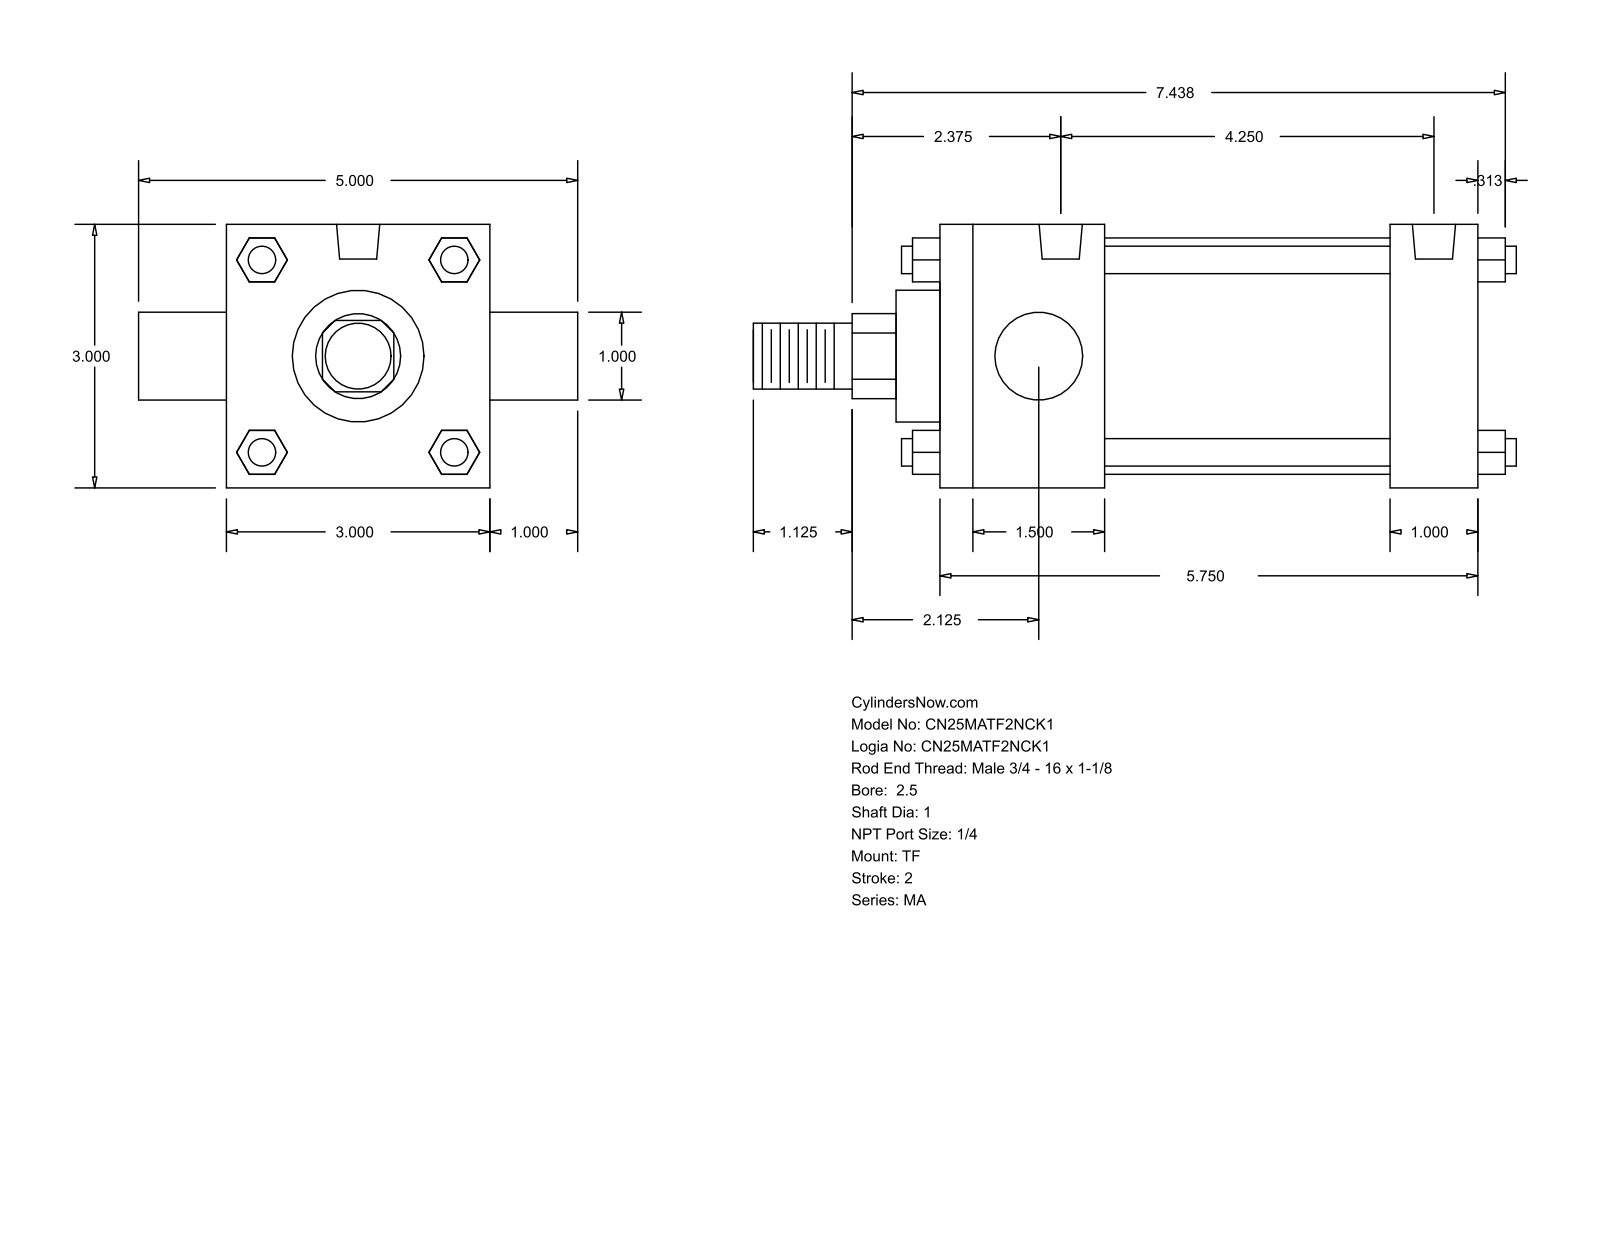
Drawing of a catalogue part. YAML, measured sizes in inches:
part_name: "MA_TF__0250_1"
step_written_by: "GSSL Pune (CONFIG_CONTROL_DESIGN)"
units: inches
bodies: {solids: 0, faces: 120, planar: 92, cylindrical: 28, other: 0}
overall_size: [8.687, 5, 3]
round_holes:
  - {diameter: 0.313, count: 3}
  - {diameter: 0.492, count: 2}
round_bosses_or_shafts:
  - {diameter: 0.313, count: 4}
  - {diameter: 1, count: 2}
  - {diameter: 2.69, count: 1}
  - {diameter: 1.5, count: 1}
  - {diameter: 0.75, count: 1}
partial_cylinders:
  - {radius: 0.484, count: 1}
face_to_face_distances: [3, 6.125, 1, 0.5, 1.875, 5.125, 3.25, 4.25, 4, 1.095]
hole_center_spacings: [4.25]
